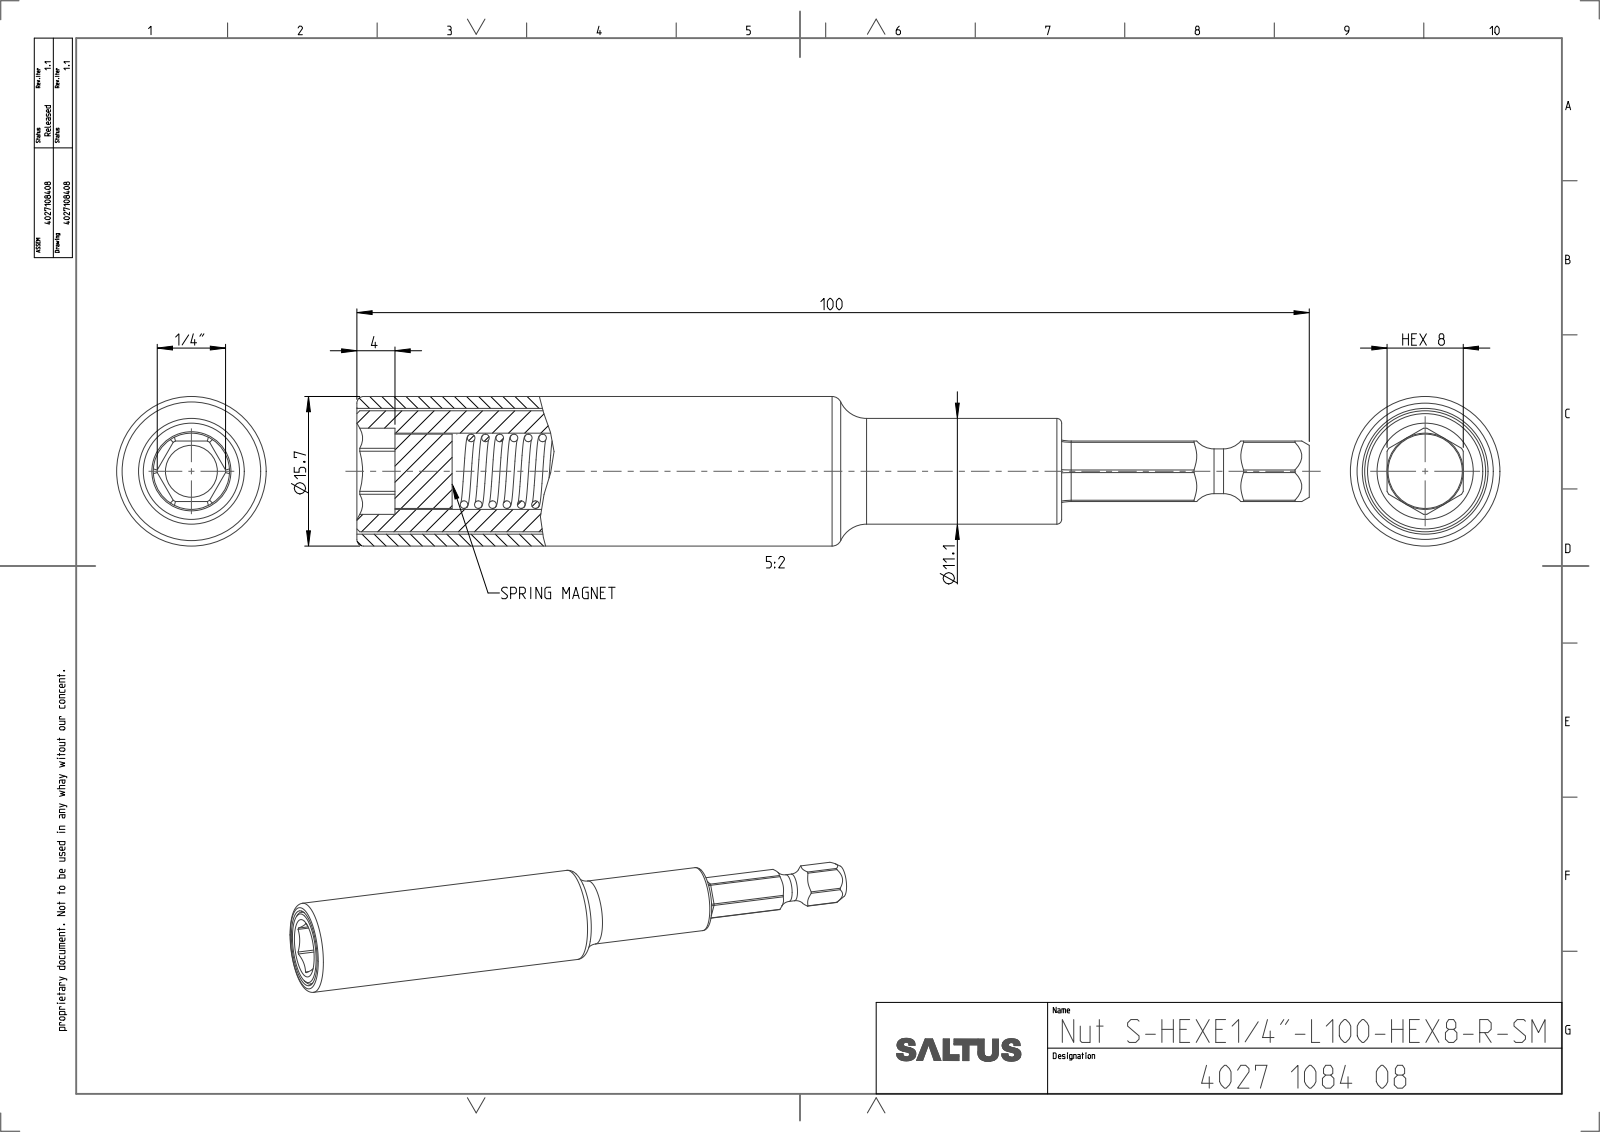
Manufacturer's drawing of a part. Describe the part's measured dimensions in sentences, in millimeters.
The part is named "4027905493; 4027299154; 4027108408_ASM". Its 3-D file was written by "CREO PARAMETRIC BY PTC INC, 2022414 (CONFIG_CONTROL_DESIGN)". It is 4 solids with 121 faces: 33 planar, 46 cylindrical and 42 other. Overall it measures 100 by 15.7 by 15.7 millimeters. Its volume is 11 078 cubic millimeters and its surface area 10 863 square millimeters. Round holes: 1 of diameter 8, 1 of diameter 8.3, 1 of diameter 13.2. Round bosses or shafts: 1 of diameter 15.7, 1 of diameter 12.7, 1 of diameter 11.1, 1 of diameter 7.8, 1 of diameter 4.7. Partial cylindrical surfaces (rounded edges, fillets, slot ends): 6 of radius 5, 1 of radius 3.59, 1 of radius 4.52. The main face-to-face distances are 6.34, 6.36, 4, 6, 10, 8, 64, 70, 74, 26.
